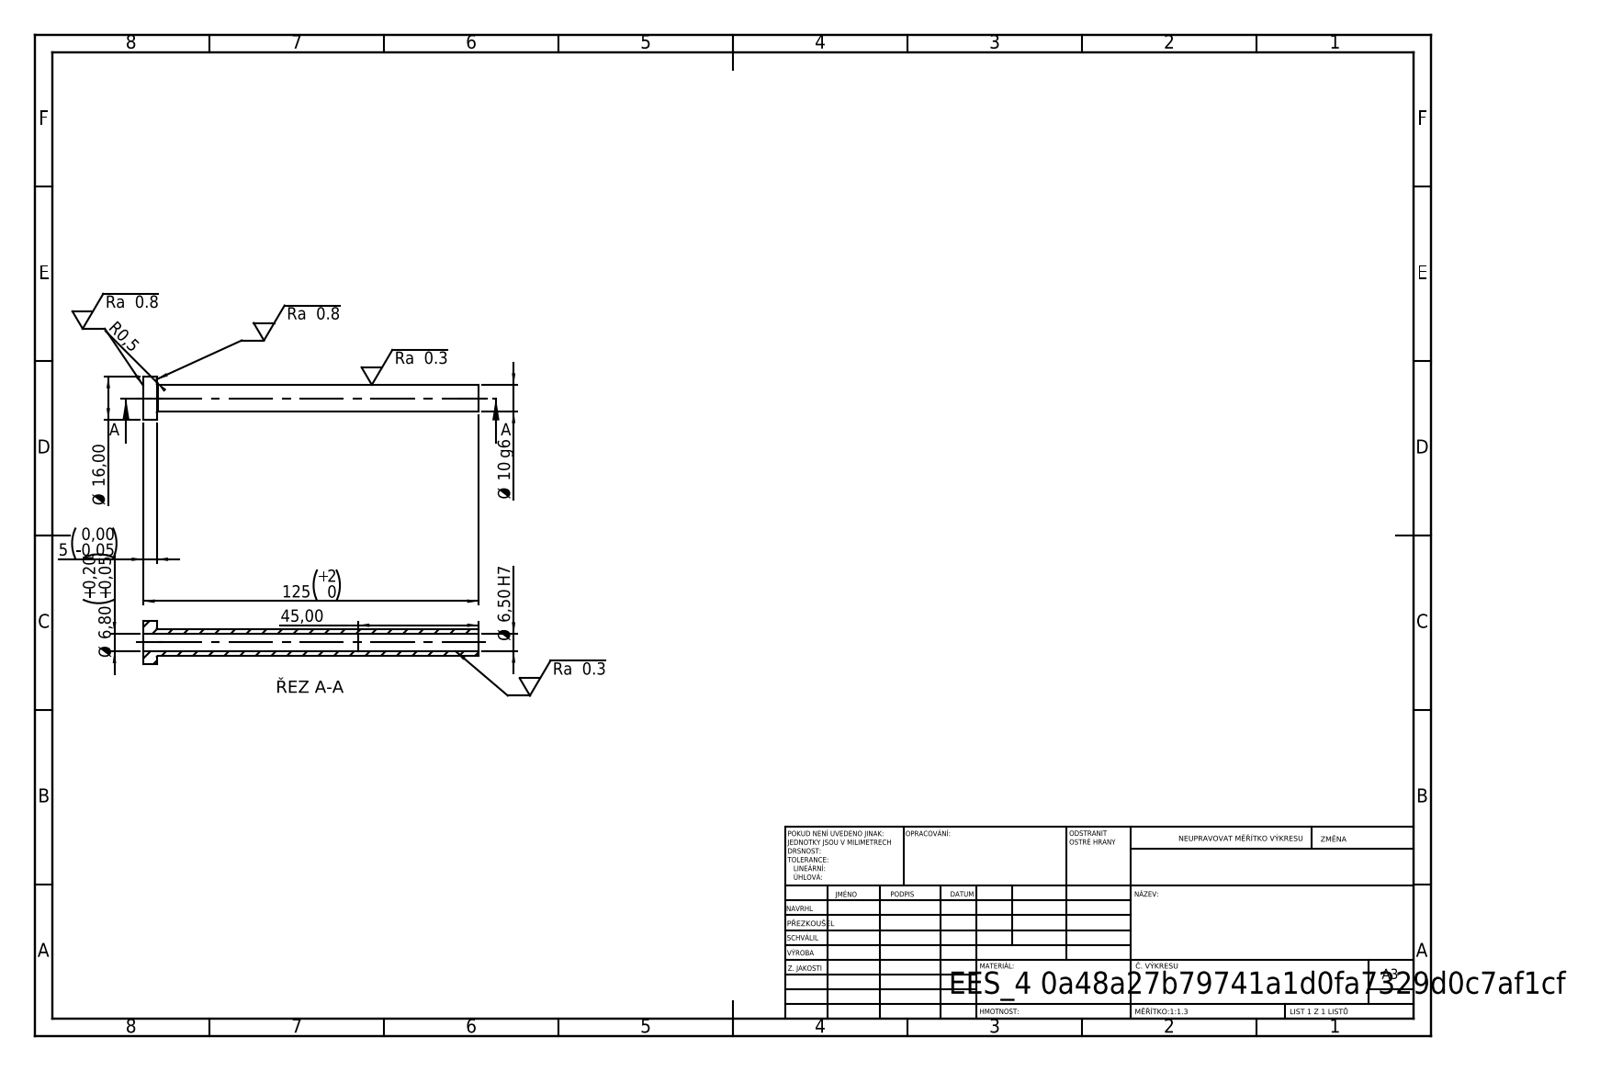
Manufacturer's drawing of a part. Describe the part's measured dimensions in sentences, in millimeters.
Its 3-D file was written by "SolidWorks 2019 (CONFIG_CONTROL_DESIGN)". It is 1 solid with 14 faces: 4 planar, 8 cylindrical and 2 other. Overall it measures 125 by 16 by 16 millimeters. Its volume is 6 033 cubic millimeters and its surface area 6 978 square millimeters. Round holes: 1 of diameter 6.5, 1 of diameter 6.8. Round bosses or shafts: 1 of diameter 16, 1 of diameter 10. The main face-to-face distances are 5, 125, 120, 80, 75, 45.
